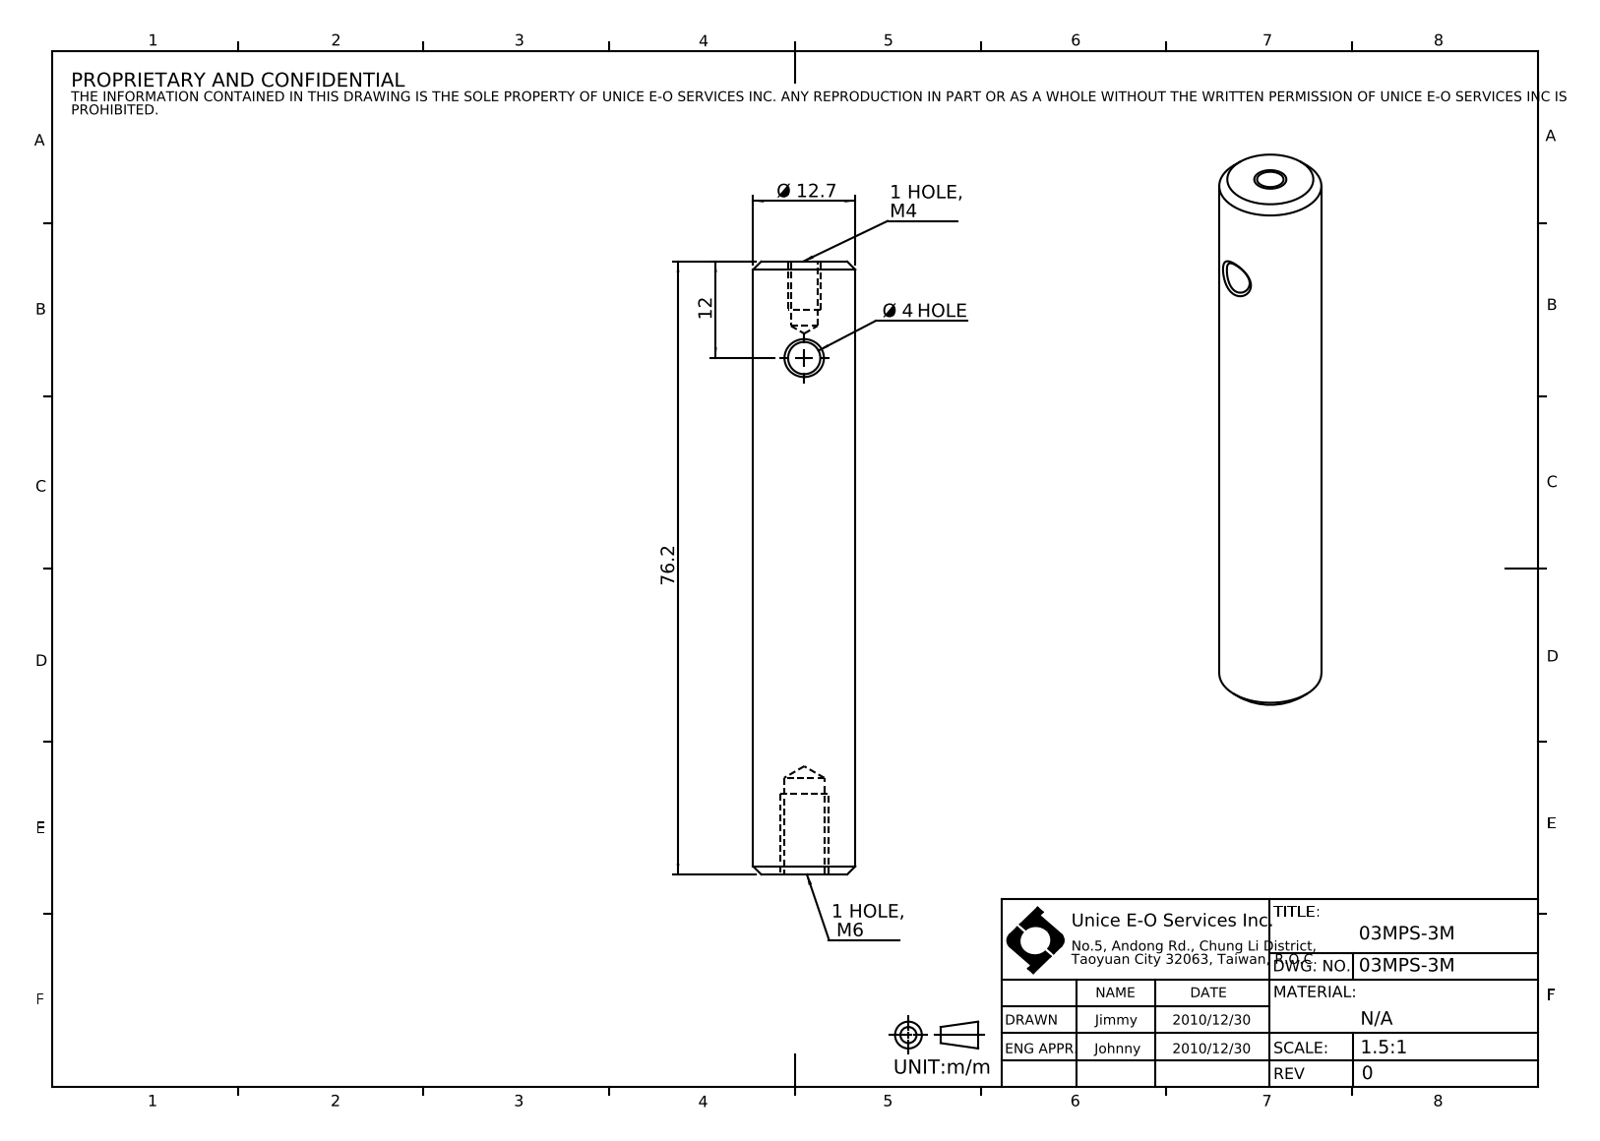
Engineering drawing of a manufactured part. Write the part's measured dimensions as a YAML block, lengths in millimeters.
part_name: "03MPS-3M"
step_written_by: "SolidWorks 2016 (CONFIG_CONTROL_DESIGN)"
units: millimeters
bodies: {solids: 1, faces: 22, planar: 2, cylindrical: 8, other: 12}
overall_size: [76.2, 12.7, 12.7]
volume: 9139
surface_area: 3644
round_holes:
  - {diameter: 3.3, count: 1}
  - {diameter: 4, count: 1}
  - {diameter: 5, count: 1}
round_bosses_or_shafts:
  - {diameter: 12.7, count: 1}
face_to_face_distances: [76.2]
